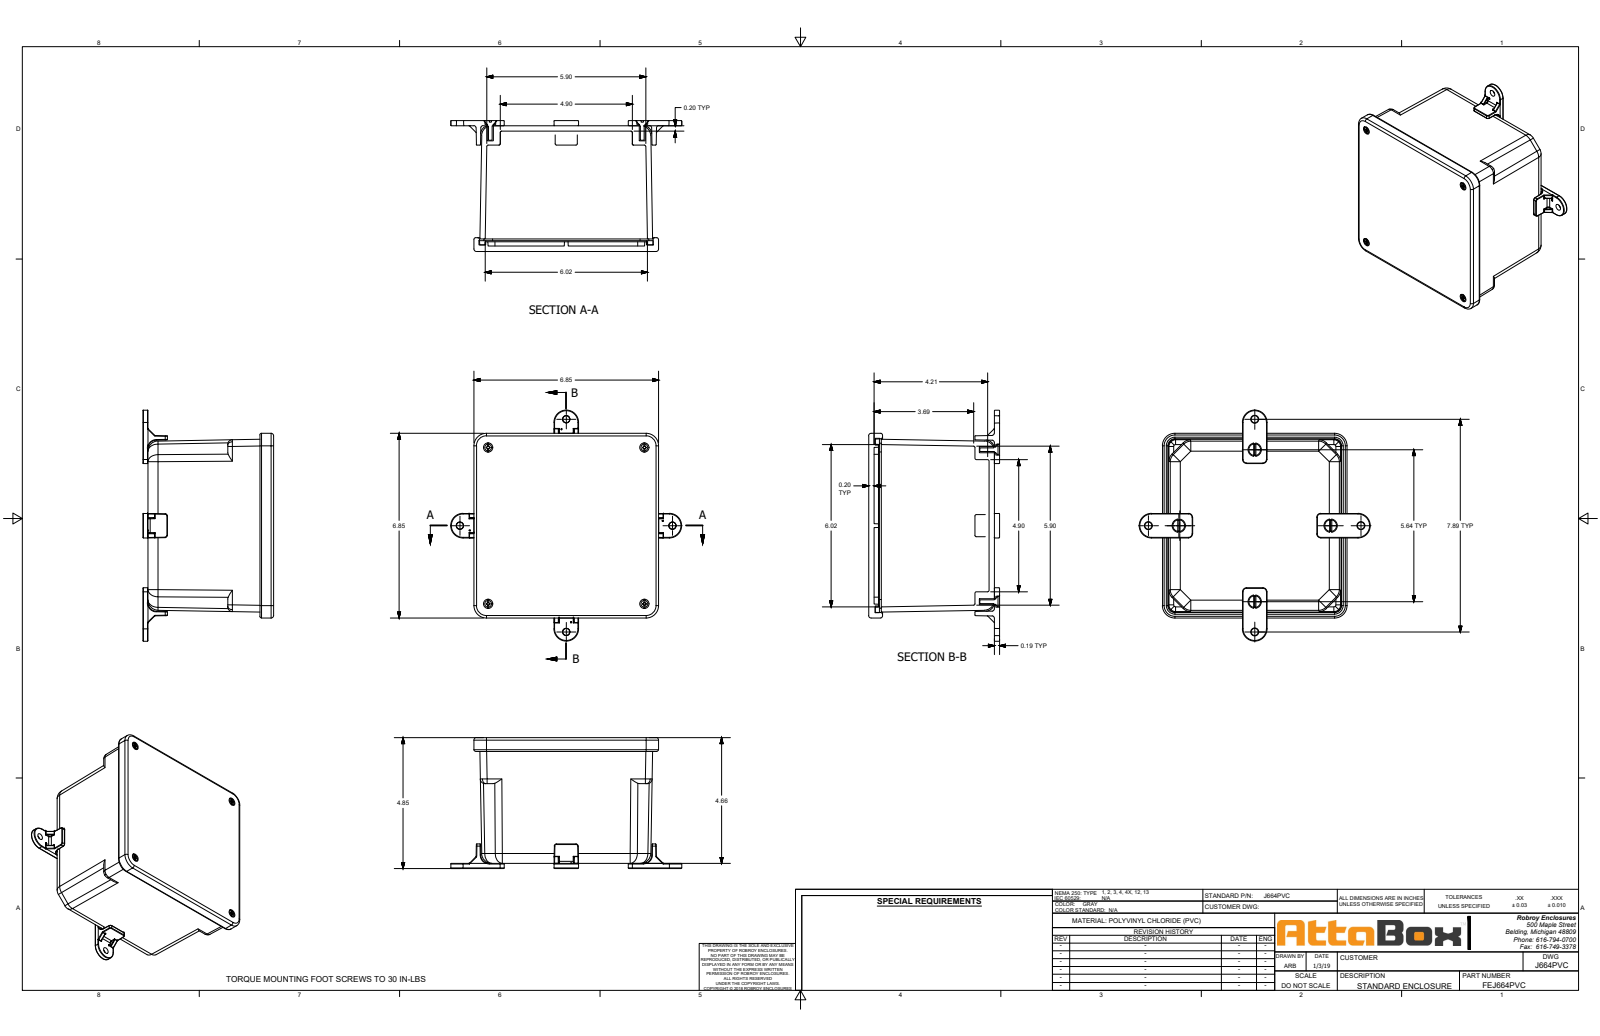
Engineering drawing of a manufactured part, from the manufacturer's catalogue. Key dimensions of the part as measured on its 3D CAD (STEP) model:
Part name (STEP PRODUCT): J664PVC
STEP written by: SolidWorks 2018 (AUTOMOTIVE_DESIGN)
Units: inches
Bodies: 23 solids, 1169 faces (465 planar, 360 cylindrical, 344 other)
Overall size (bounding box): 8.568 × 8.568 × 4.854
Volume: 42.59 in³ · Surface area: 444.4 in²
Round holes (diameter × count): ⌀0.2 ×8, ⌀0.13 ×4, ⌀0.14 ×4, ⌀0.175 ×4, ⌀0.22 ×4, ⌀0.245 ×4, ⌀0.276 ×4, ⌀0.33 ×4, ⌀0.345 ×4
Round bosses / shafts (diameter × count): ⌀0.354 ×4, ⌀0.224 ×4, ⌀0.187 ×4, ⌀0.177 ×4, ⌀0.325 ×3, ⌀0.325 ×1
Partial cylindrical surfaces — rounded edges, fillets, slot ends (radius × count): R0.02 ×84, R0.25 ×24, R0.005 ×16, R0.05 ×16, R0.375 ×16, R0.08 ×12, R0.094 ×12, R0.03 ×8
Main face-to-face distances: 0.195, 0.2, 4.464, 4.664, 4.264, 4.422, 4.222, 0.042, 0.242, 4.265
Hole centre spacings: 2.901, 6.412, 5.8, 5.813, 3.987, 0.013, 2.902, 2.914
